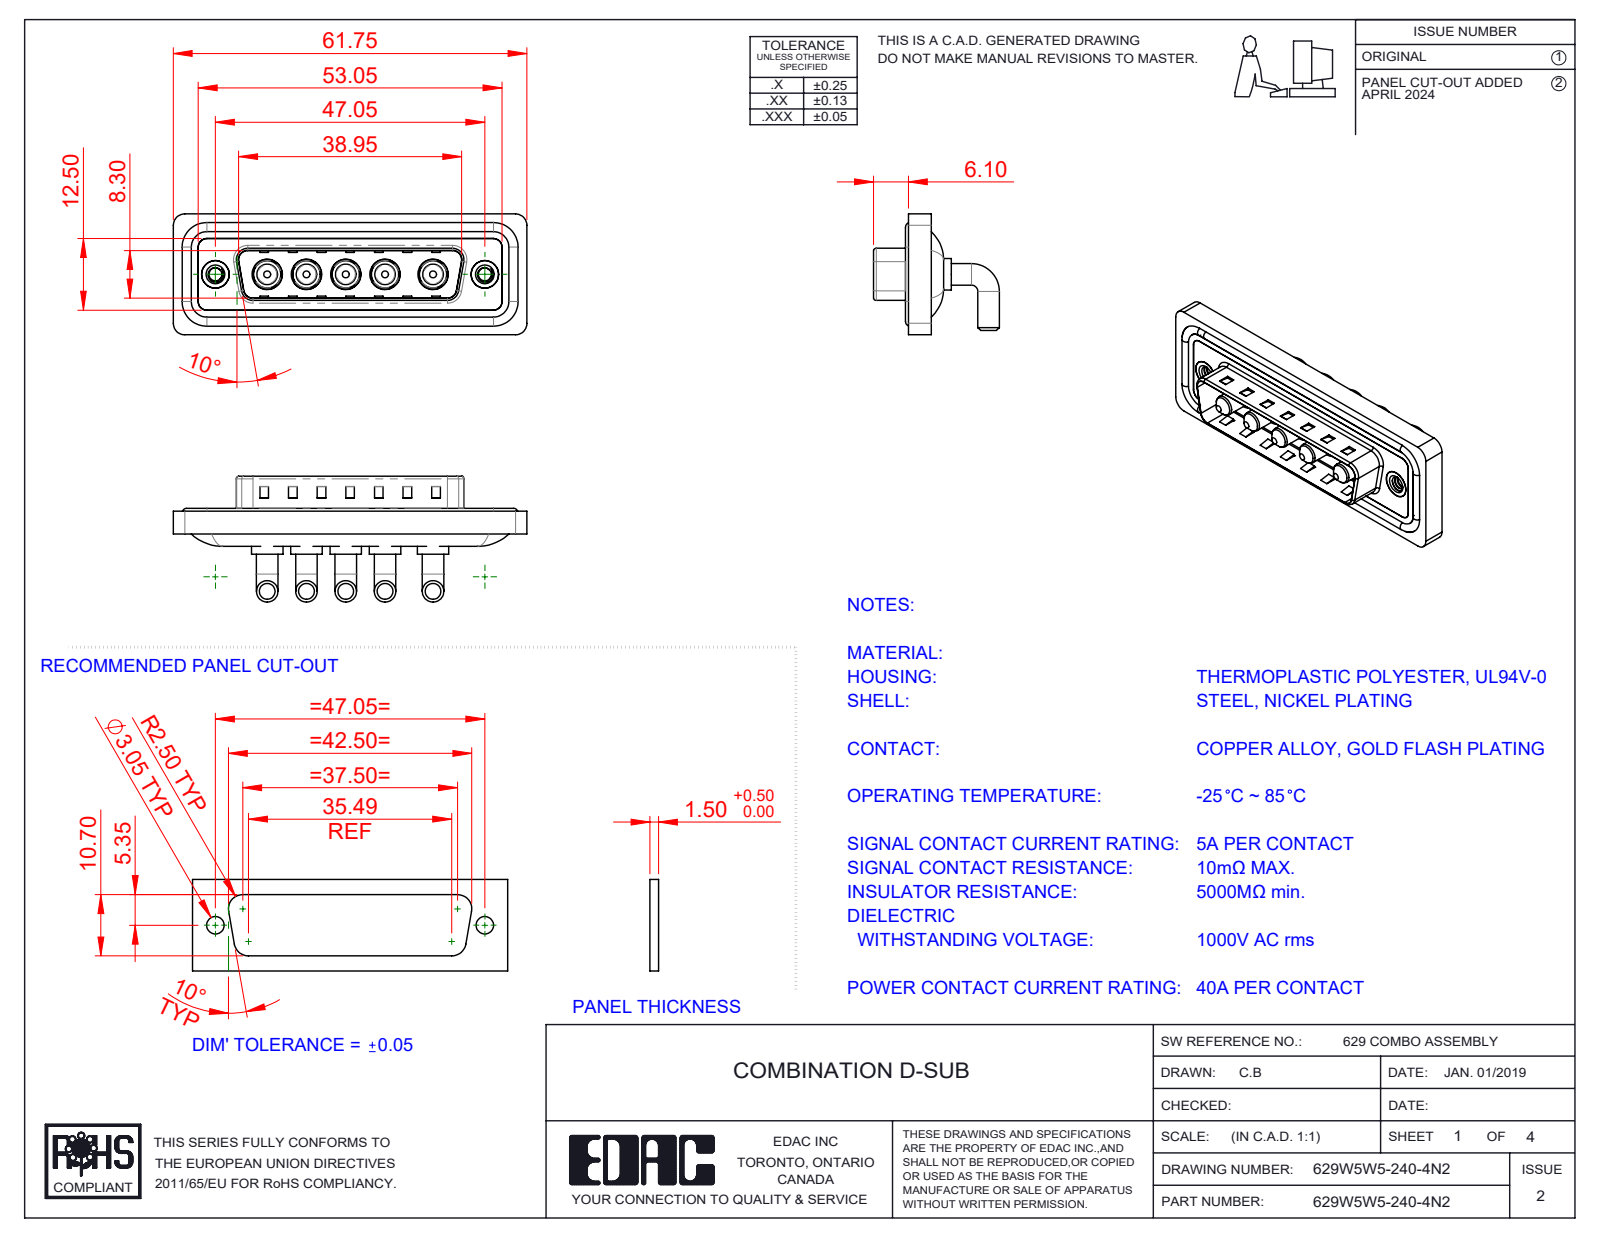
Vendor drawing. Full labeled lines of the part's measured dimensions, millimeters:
Part name (STEP PRODUCT): 629Combo Housing_5W5; 629Combo Shell Front_25 Contacts; 629Combo Threaded Rivet_2; 629W5W5-240-4N2 (+3 more)
STEP written by: SolidWorks 2023 (CONFIG_CONTROL_DESIGN)
Units: millimetres
Bodies: 17 solids, 698 faces (259 planar, 293 cylindrical, 146 other)
Overall size (bounding box): 61.75 × 21.98 × 21.1
Volume: 8 178 mm³ · Surface area: 12 492 mm²
Round holes (diameter × count): ⌀4.85 ×5, ⌀5.3 ×5, ⌀2.26 ×2, ⌀4 ×2, ⌀4.8 ×2, ⌀5 ×2
Round bosses / shafts (diameter × count): ⌀3.75 ×10, ⌀5.5 ×5, ⌀5.2 ×5, ⌀4.75 ×5, ⌀3.6 ×5, ⌀1.6 ×4, ⌀4.9 ×2
Partial cylindrical surfaces — rounded edges, fillets, slot ends (radius × count): R1.5 ×18, R2 ×18, R0.5 ×8, R1.6 ×8, R2.1 ×5, R0.25 ×4, R0.6 ×4, R0.65 ×4
Main face-to-face distances: 0.4, 2.9, 0.8, 4.5, 4.1, 1.1, 2.1, 3.1, 6, 2.5
Hole centre spacings: 6.86, 13.73, 6.85, 6.87, 8.37, 8.38, 9.04, 9.05
